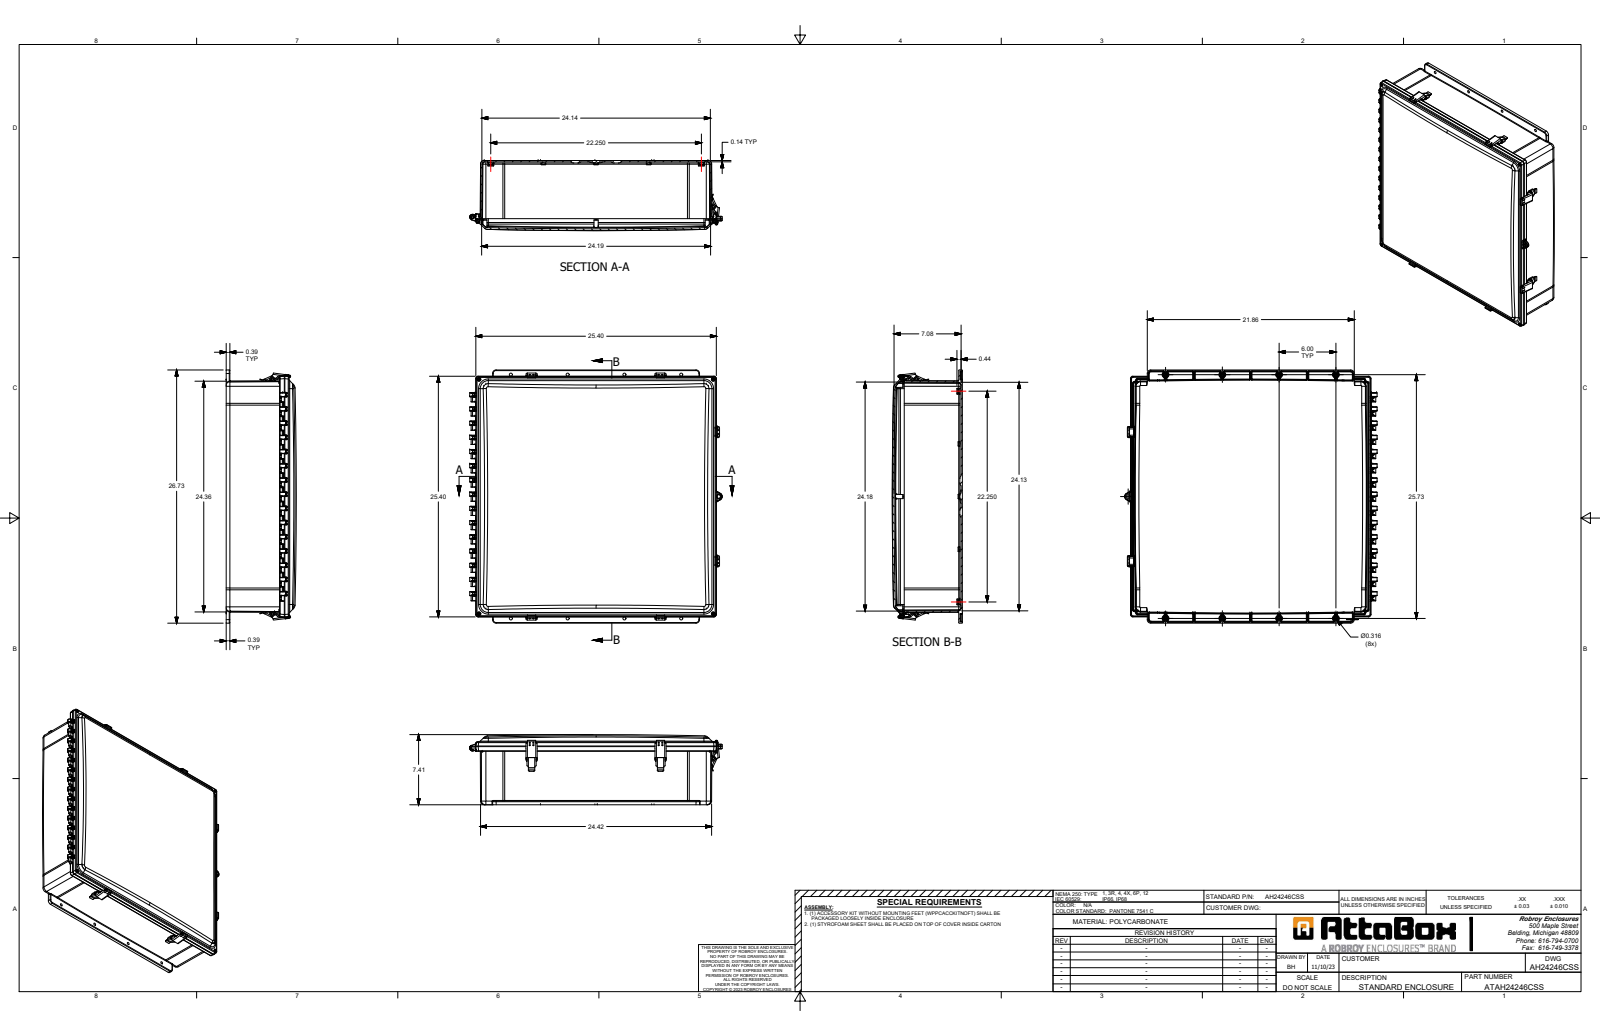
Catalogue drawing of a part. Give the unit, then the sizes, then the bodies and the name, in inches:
Units: inches
Overall size (bounding box): 26.73 × 26.676 × 7.408
Round holes (diameter × count): ⌀0.187 ×21, ⌀0.316 ×8, ⌀0.195 ×4, ⌀0.25 ×4, ⌀0.296 ×4, ⌀0.39 ×4, ⌀0.327 ×1, ⌀0.375 ×1, ⌀0.45 ×1
Round bosses / shafts (diameter × count): ⌀0.487 ×21, ⌀0.625 ×4, ⌀0.313 ×1
Partial cylindrical surfaces — rounded edges, fillets, slot ends (radius × count): R0.035 ×121, R0.02 ×24, R0.052 ×24, R0.25 ×8, R10.14 ×8, R0.375 ×5, R0.09 ×4, R0.36 ×4
Main face-to-face distances: 0.14, 24.23, 6, 6.14, 0.115, 24.115, 0.5, 5.64, 5.5, 0.389
Hole centre spacings: 12.438, 7.867, 5.563, 17.59, 11.125, 5.562, 11.125, 20.056
Volume: 328.6 in³ · Surface area: 4 187 in²
Bodies: 14 solids, 1614 faces (653 planar, 433 cylindrical, 528 other)
Part name (STEP PRODUCT): AH24246SS
STEP written by: SolidWorks 2023 (AUTOMOTIVE_DESIGN)
